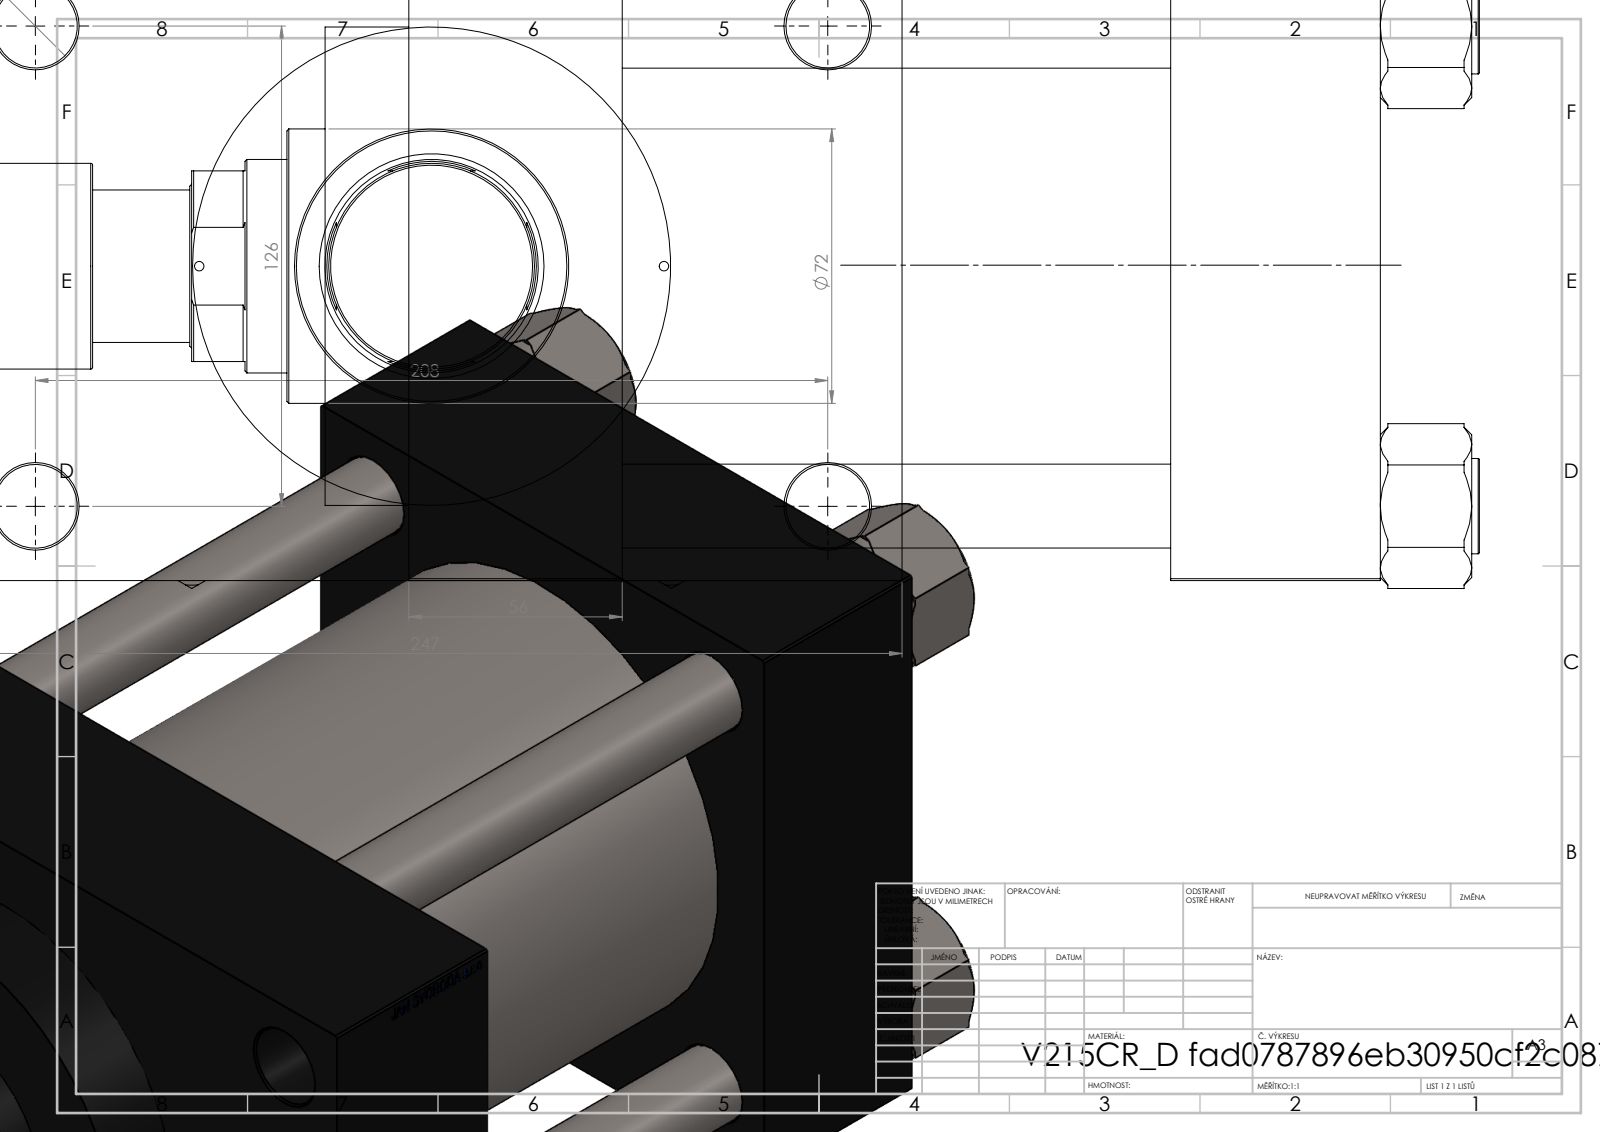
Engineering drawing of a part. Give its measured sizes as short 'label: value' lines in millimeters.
name: NUT_M5_D; V215CR_D_TYCINKA; V215CR_VCP_D; V215CR_ROD_END_F (+2 more)
written by: SolidWorks 2019 (CONFIG_CONTROL_DESIGN)
unit: mm
bodies: 12 solids, 1168 faces (550 planar, 94 cylindrical, 524 other)
size: 390 × 247 × 169.14
volume: 5 328 000 mm³; area: 622 075 mm²
holes: 8× ⌀22, 2× ⌀2.5, 2× ⌀7, 2× ⌀32.24, 2× ⌀45, 1× ⌀40.5, 1× ⌀56, 1× ⌀59, 1× ⌀96, 1× ⌀125, 1× ⌀125.5
bosses: 4× ⌀25, 1× ⌀131, 1× ⌀72, 1× ⌀54, 1× ⌀40
face distances: 165, 144, 55, 199, 56, 255, 200, 41, 206, 233.74
hole spacings: 41.05, 62.98, 76.28, 89.02, 121.59, 125.9, 132.47, 139.02
